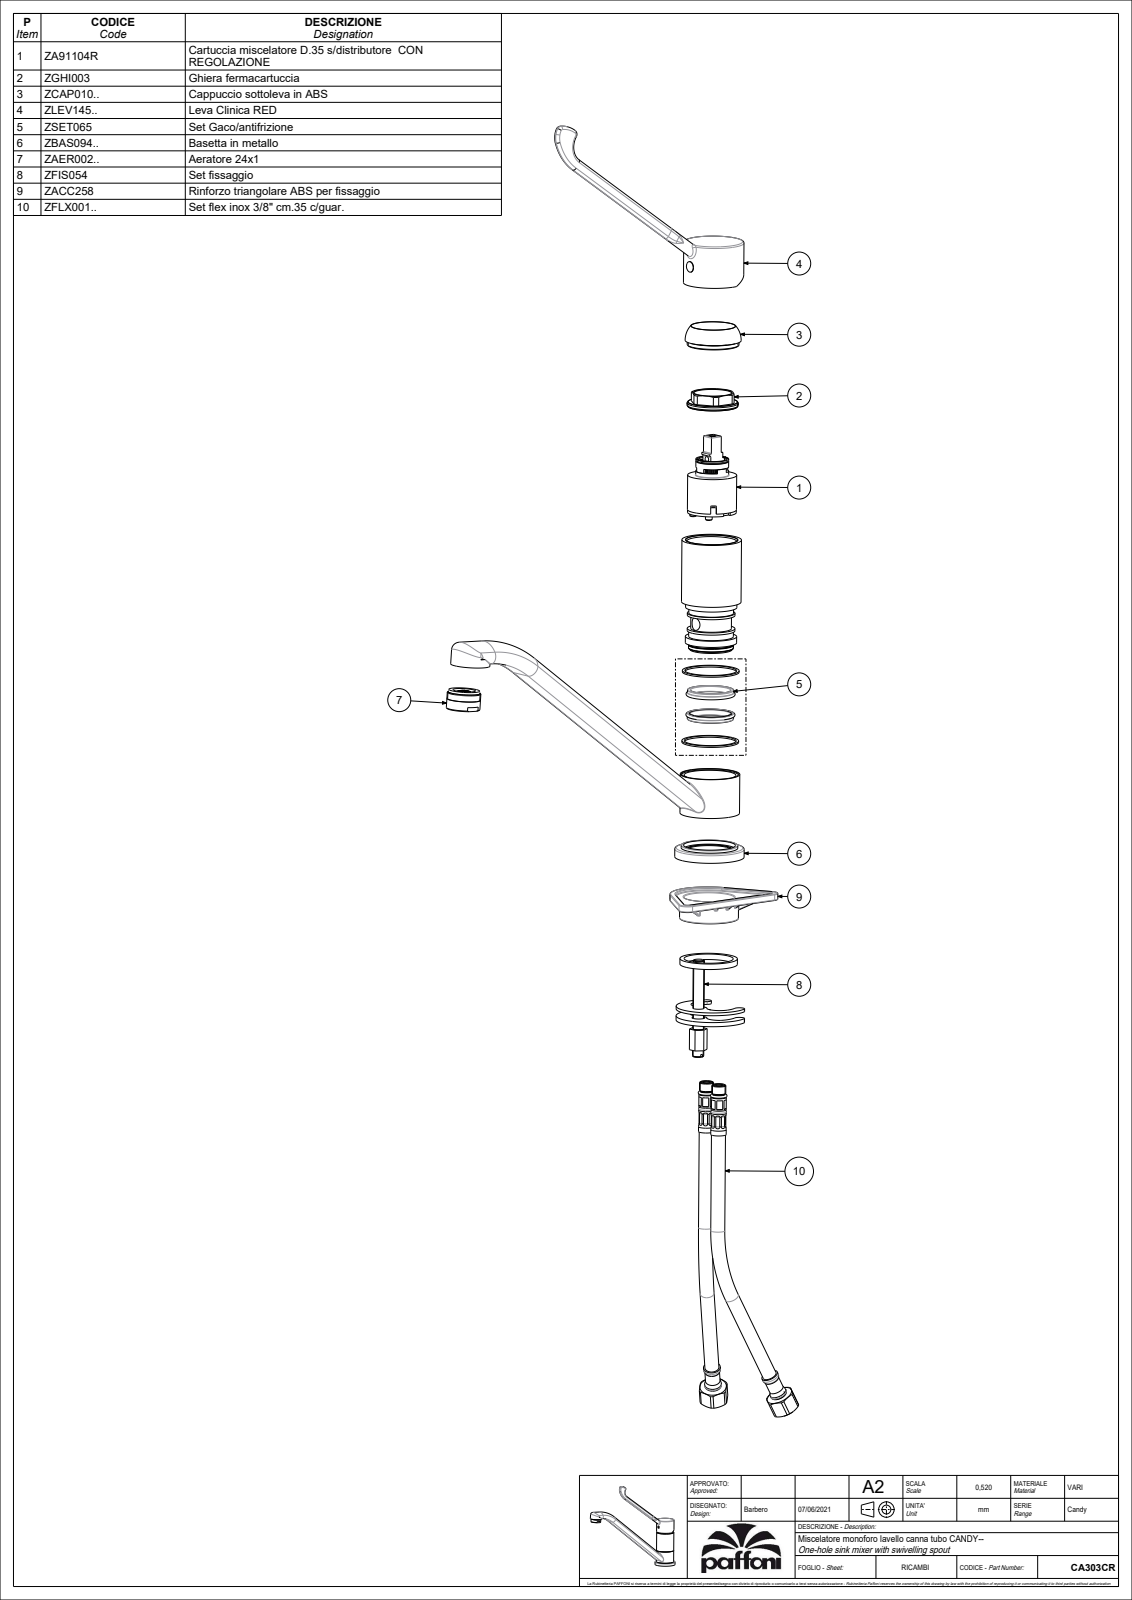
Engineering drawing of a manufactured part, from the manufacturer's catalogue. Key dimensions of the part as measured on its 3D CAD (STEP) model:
Part name (STEP PRODUCT): CA303CR
STEP written by: CREO PARAMETRIC BY PTC INC, 2020044 (CONFIG_CONTROL_DESIGN)
Units: millimetres
Bodies: 2 solids, 436 faces (100 planar, 180 cylindrical, 156 other)
Overall size (bounding box): 258.72 × 212.08 × 49.5
Volume: 114 459 mm³ · Surface area: 88 808 mm²
Round holes (diameter × count): ⌀9 ×4, ⌀8 ×3, ⌀5 ×2, ⌀11 ×2, ⌀3 ×1, ⌀6.8 ×1, ⌀16 ×1, ⌀20 ×1, ⌀21 ×1, ⌀23 ×1, ⌀31 ×1, ⌀31.5 ×1
Round bosses / shafts (diameter × count): ⌀49.5 ×1, ⌀43 ×1, ⌀42.5 ×1, ⌀40.4 ×1, ⌀36.6 ×1, ⌀34 ×1, ⌀31.9 ×1, ⌀30 ×1
Partial cylindrical surfaces — rounded edges, fillets, slot ends (radius × count): R0.5 ×39, R2 ×4, R3 ×2, R4 ×2, R13 ×2, R18.3 ×2, R25.63 ×2, R3.5 ×1
Main face-to-face distances: 1, 112.3, 112.27, 4.5, 90.87, 5.8, 45.5, 106.8, 45.4, 45.37
Hole centre spacings: 0.5, 8.32, 8.6, 9.06, 10.42, 11.6, 12, 13.45
